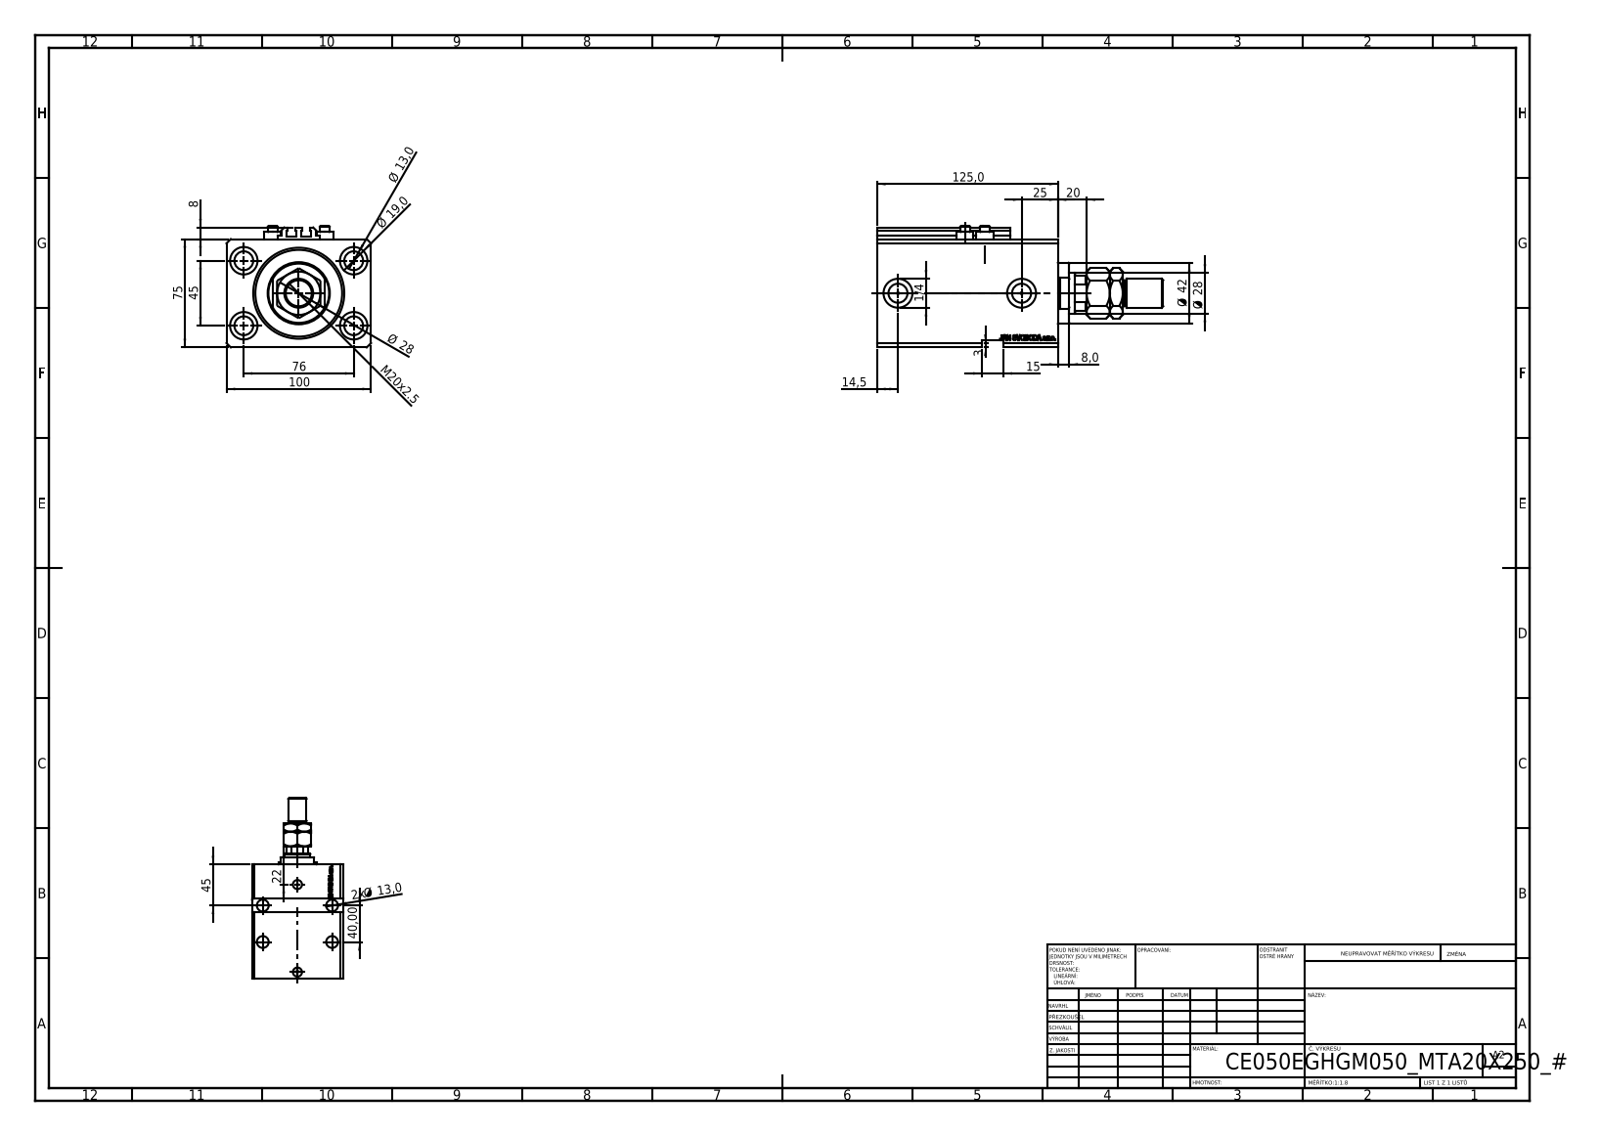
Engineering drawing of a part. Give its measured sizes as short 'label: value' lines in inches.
name: ALLEN BOLT V250CE; V250CE_VC_E; V250CE_E_Body; MTA (+1 more)
written by: SolidWorks 2019 (CONFIG_CONTROL_DESIGN)
unit: in
bodies: 9 solids, 1157 faces (550 planar, 150 cylindrical, 457 other)
size: 7.795 × 3.937 × 3.307
volume: 48.62 in³; area: 242.1 in²
holes: 8× ⌀0.512, 4× ⌀0.049, 4× ⌀0.157, 4× ⌀0.748, 2× ⌀0.394, 2× ⌀0.518, 2× ⌀0.787, 1× ⌀0.728, 1× ⌀1.102, 1× ⌀1.969, 1× ⌀2.48
bosses: 4× ⌀0.457, 4× ⌀0.276, 1× ⌀1.654, 1× ⌀0.787, 1× ⌀0.709
rounds: 10× R0.008, 1× R0.531
face distances: 2.953, 3.937, 0.787, 4.921, 0.469, 4.453, 4.134, 3.665, 2.756, 0.118
hole spacings: 1.739, 2.992, 0.535, 0.816, 1.086, 1.142, 1.324, 1.417
